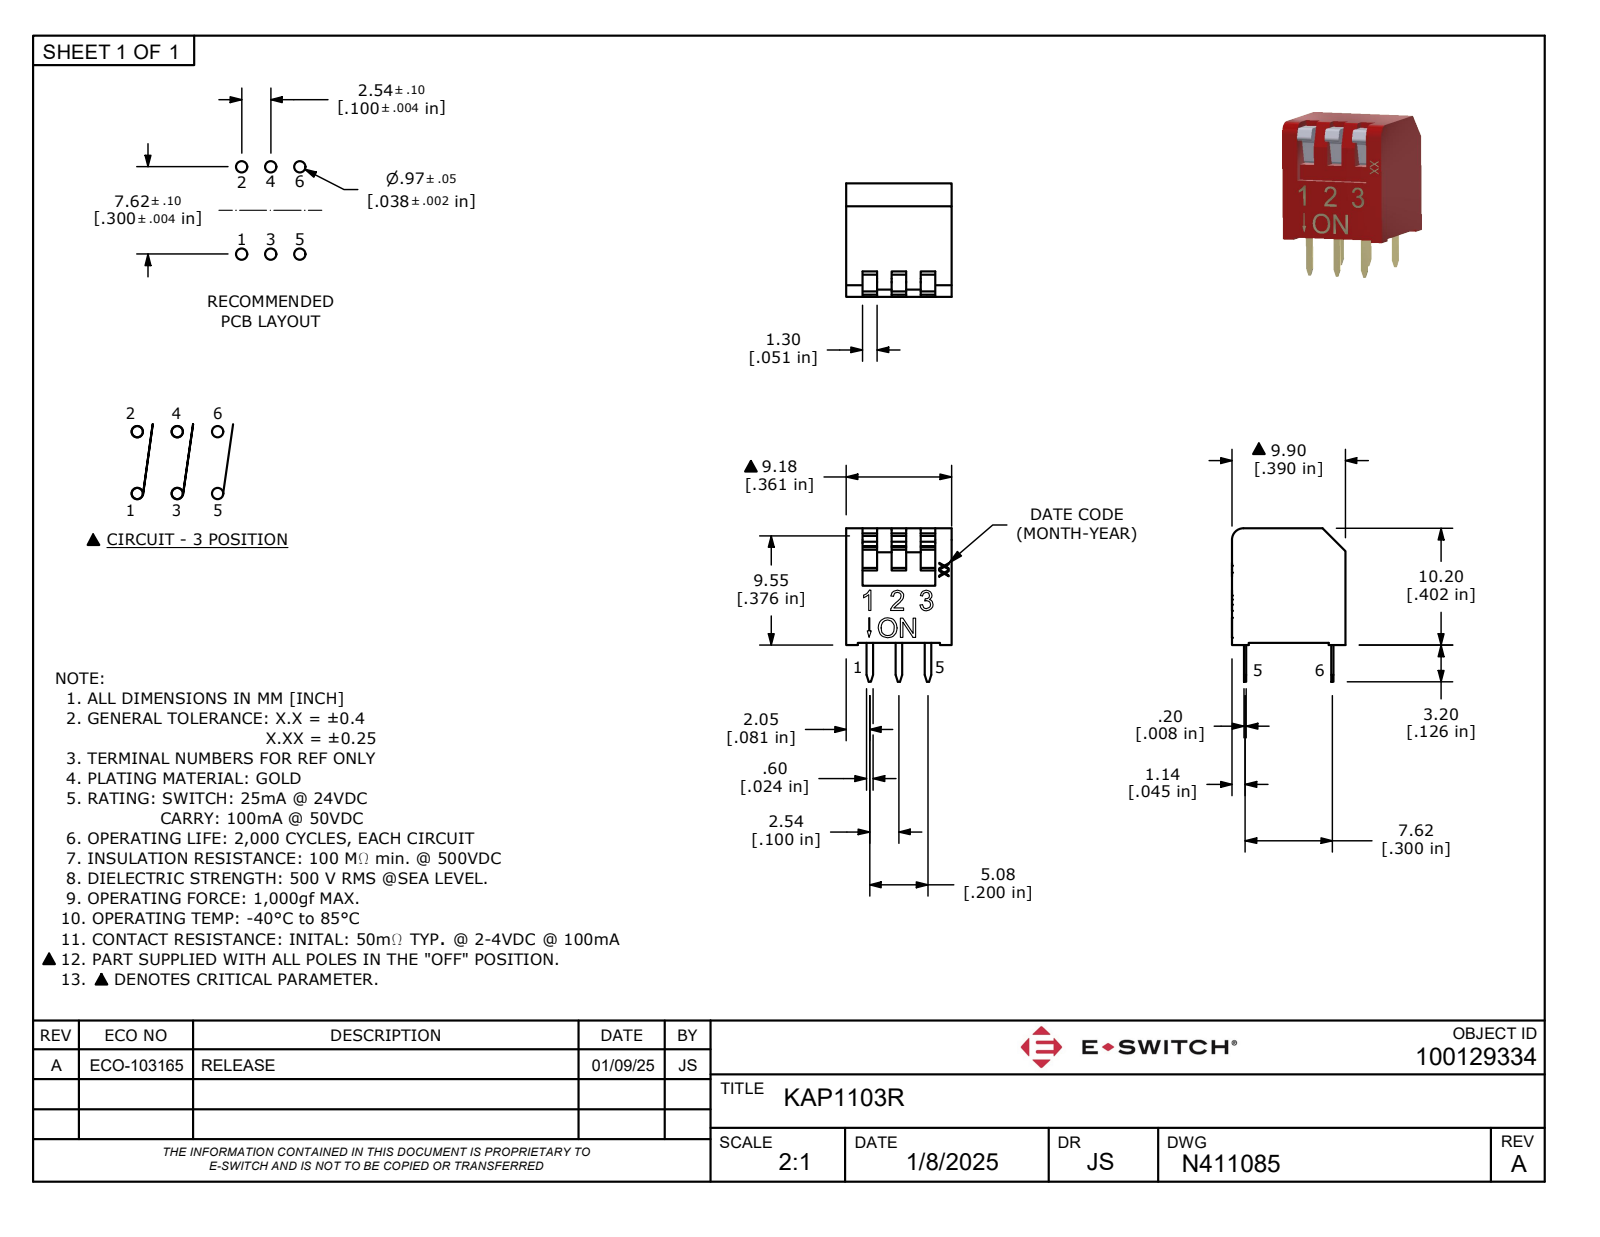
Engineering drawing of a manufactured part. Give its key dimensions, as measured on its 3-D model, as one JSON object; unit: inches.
{"part_name": "P:\\\\E-Switch Secure\\\\3D_MODELS_STP_FORMAT\\\\KAP1103R.stp", "step_written_by": "ACIS (CONFIG_CONTROL_DESIGN)", "units": "inches", "bodies": {"solids": 7, "faces": 230, "planar": 187, "cylindrical": 10, "other": 33}, "overall_size": [0.531, 0.426, 0.361], "volume_in3": 0.056, "surface_area_in2": 1.053, "partial_cylinders_radius": [[0.01, 2], [0.039, 1], [0.269, 1]], "face_to_face_distances": [0.361, 0.394, 0.425, 0.035, 0.327, 0.1, 0.139, 0.051, 0.3, 0.07]}
